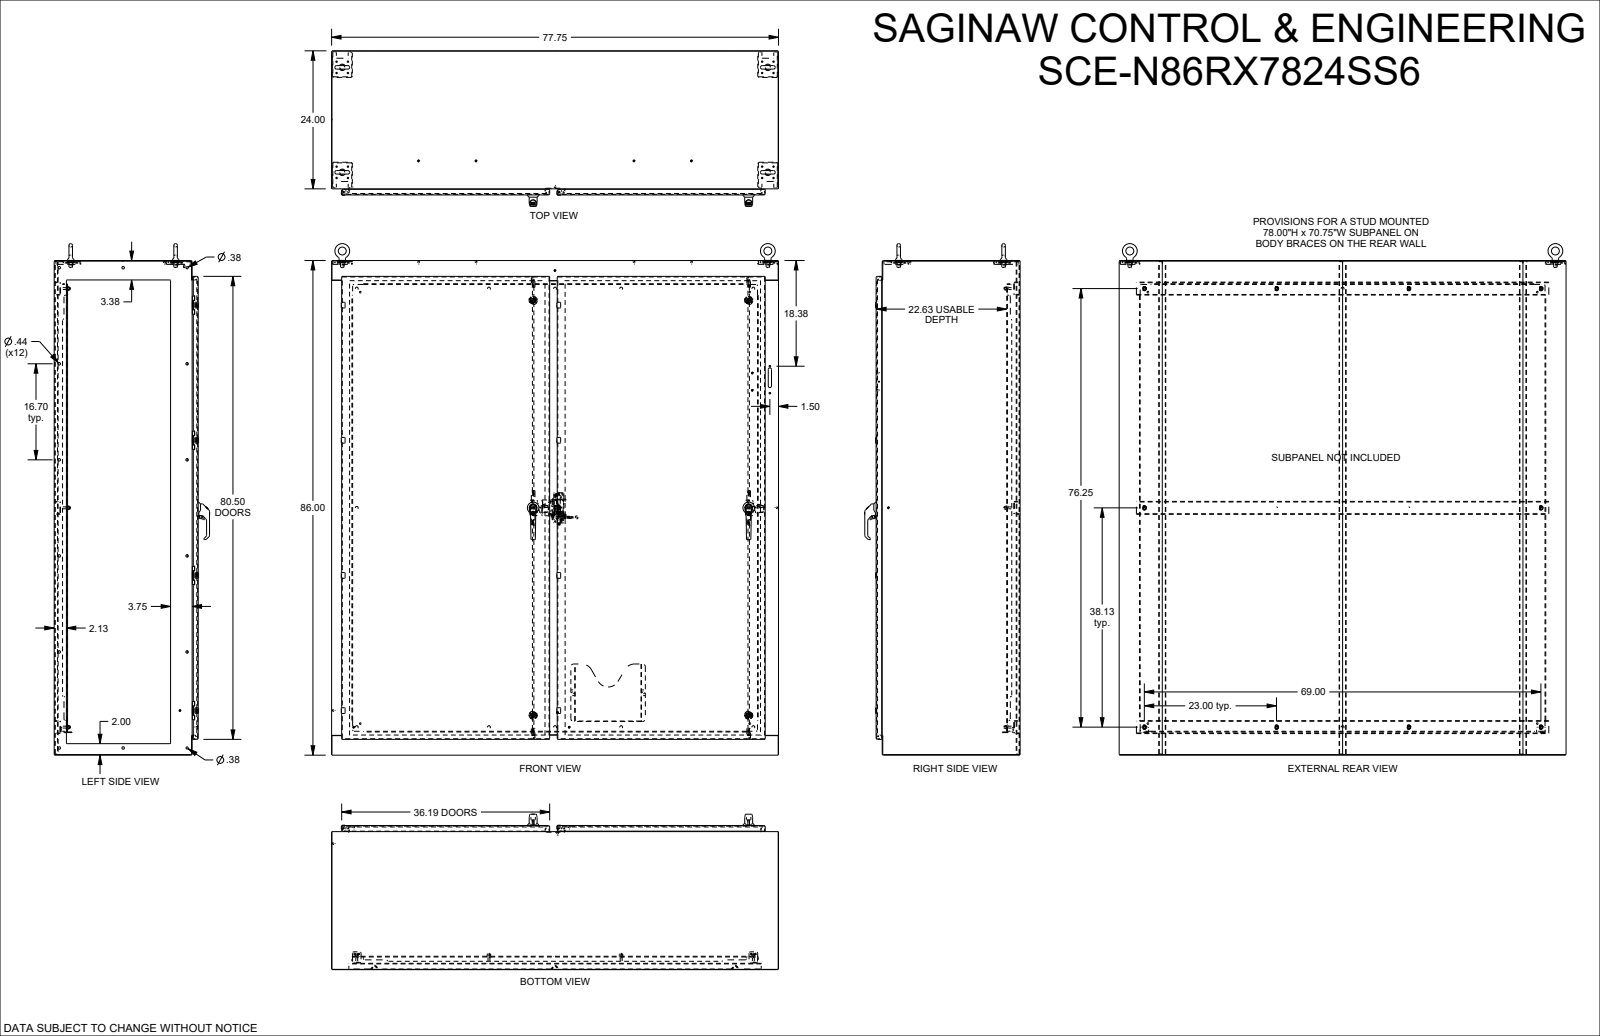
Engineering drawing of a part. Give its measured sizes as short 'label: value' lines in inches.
name: SCE-N86RX7824
written by: SolidWorks 2023 (AUTOMOTIVE_DESIGN)
unit: in
bodies: 55 solids, 8334 faces (3463 planar, 2938 cylindrical, 1933 other)
size: 88.975 × 77.75 × 27.046
volume: 2 392 in³; area: 45 538 in²
holes: 24× ⌀0.25, 18× ⌀0.375, 16× ⌀0.205, 16× ⌀0.244, 12× ⌀0.437, 8× ⌀0.04, 8× ⌀0.17, 8× ⌀0.218, 4× ⌀0.256, 4× ⌀0.343, 4× ⌀0.344, 4× ⌀0.36
bosses: 24× ⌀0.17, 19× ⌀0.25, 16× ⌀0.24, 10× ⌀0.196, 4× ⌀1.4, 4× ⌀1.267, 4× ⌀1.173, 4× ⌀0.6
rounds: 229× R0.03, 166× R0.015, 144× R0.164, 144× R0.198, 96× R0.125, 59× R0.04, 57× R0.02, 48× R0.02
face distances: 0.104, 24.954, 24.85, 25.058, 85.896, 23.896, 1.058, 86, 85.792, 23.792
hole spacings: 23.5, 1.979, 16.7, 27.82, 37.5, 47, 1.4, 44.255
